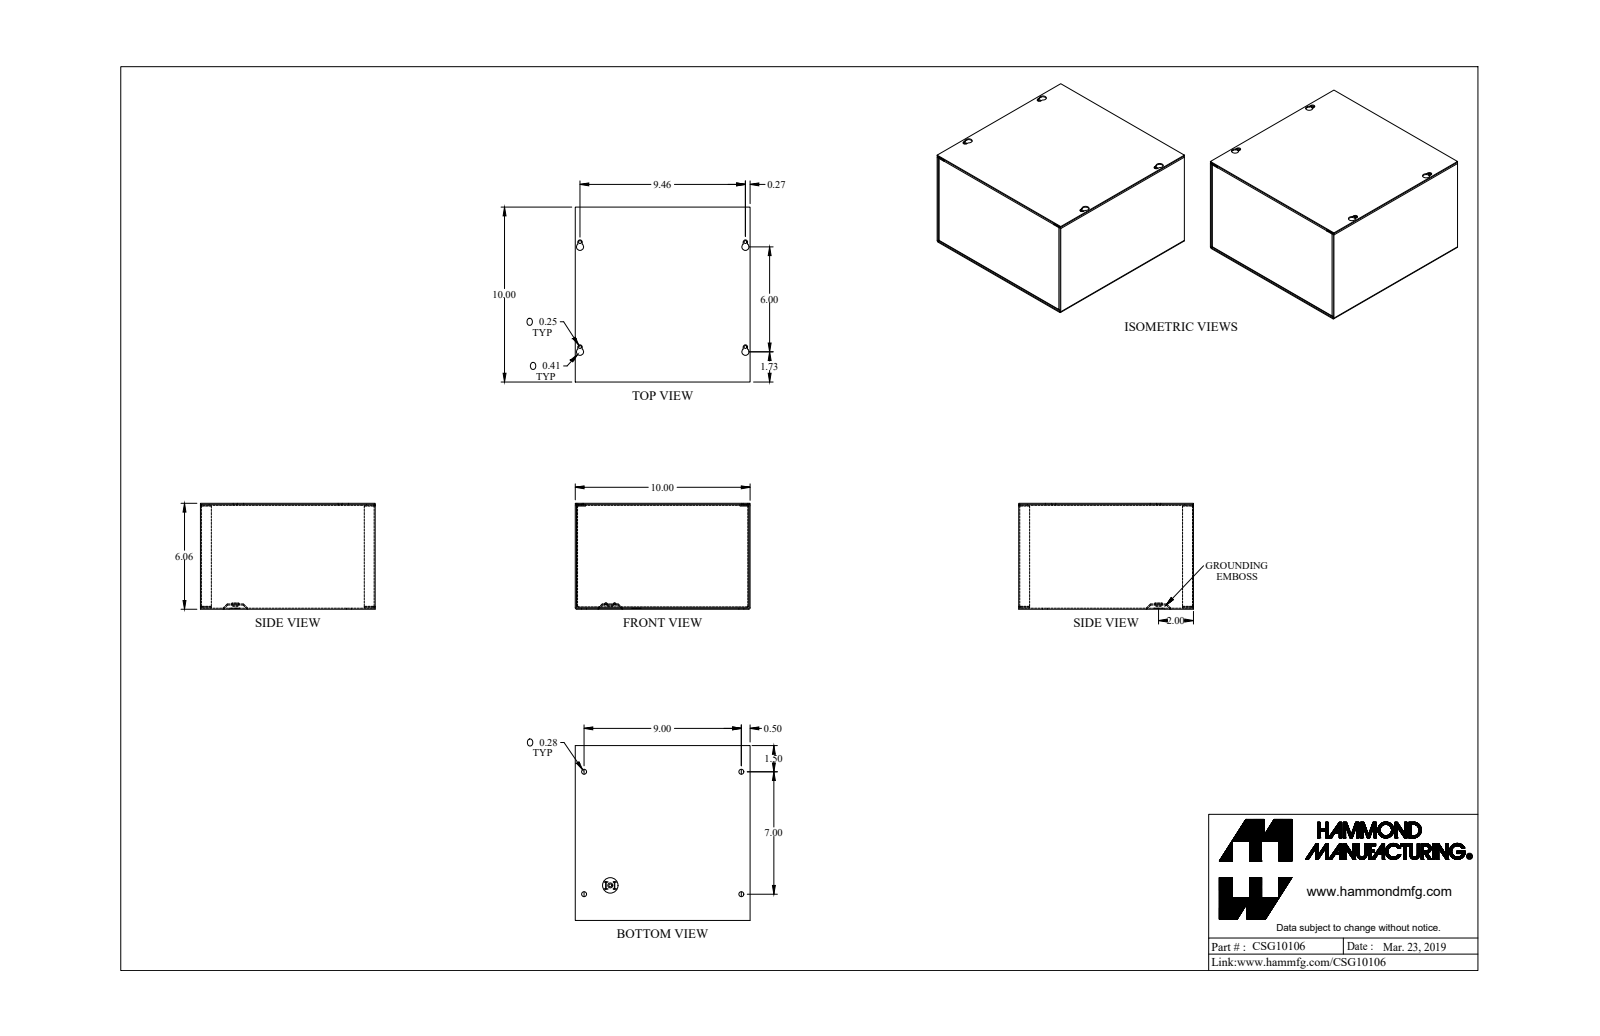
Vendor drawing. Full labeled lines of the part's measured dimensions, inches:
Part name (STEP PRODUCT): CSG10106_Default
STEP written by: SolidWorks 2019 (CONFIG_CONTROL_DESIGN)
Units: inches
Bodies: 4 solids, 205 faces (125 planar, 72 cylindrical, 8 other)
Overall size (bounding box): 10 × 10 × 6.057
Volume: 26.96 in³ · Surface area: 957 in²
Round holes (diameter × count): ⌀0.17 ×5, ⌀0.281 ×4, ⌀0.5 ×1
Round bosses / shafts (diameter × count): ⌀0.492 ×1, ⌀0.284 ×1
Partial cylindrical surfaces — rounded edges, fillets, slot ends (radius × count): R0.029 ×12, R0.086 ×12, R0.057 ×8, R0.125 ×4, R0.203 ×4
Main face-to-face distances: 0.057, 9.943, 6, 10, 9.886, 5.943, 6.057, 0.07, 9.873, 0.08
Hole centre spacings: 0.55, 6.504, 9.243, 11.289, 6, 7, 9, 9.46
